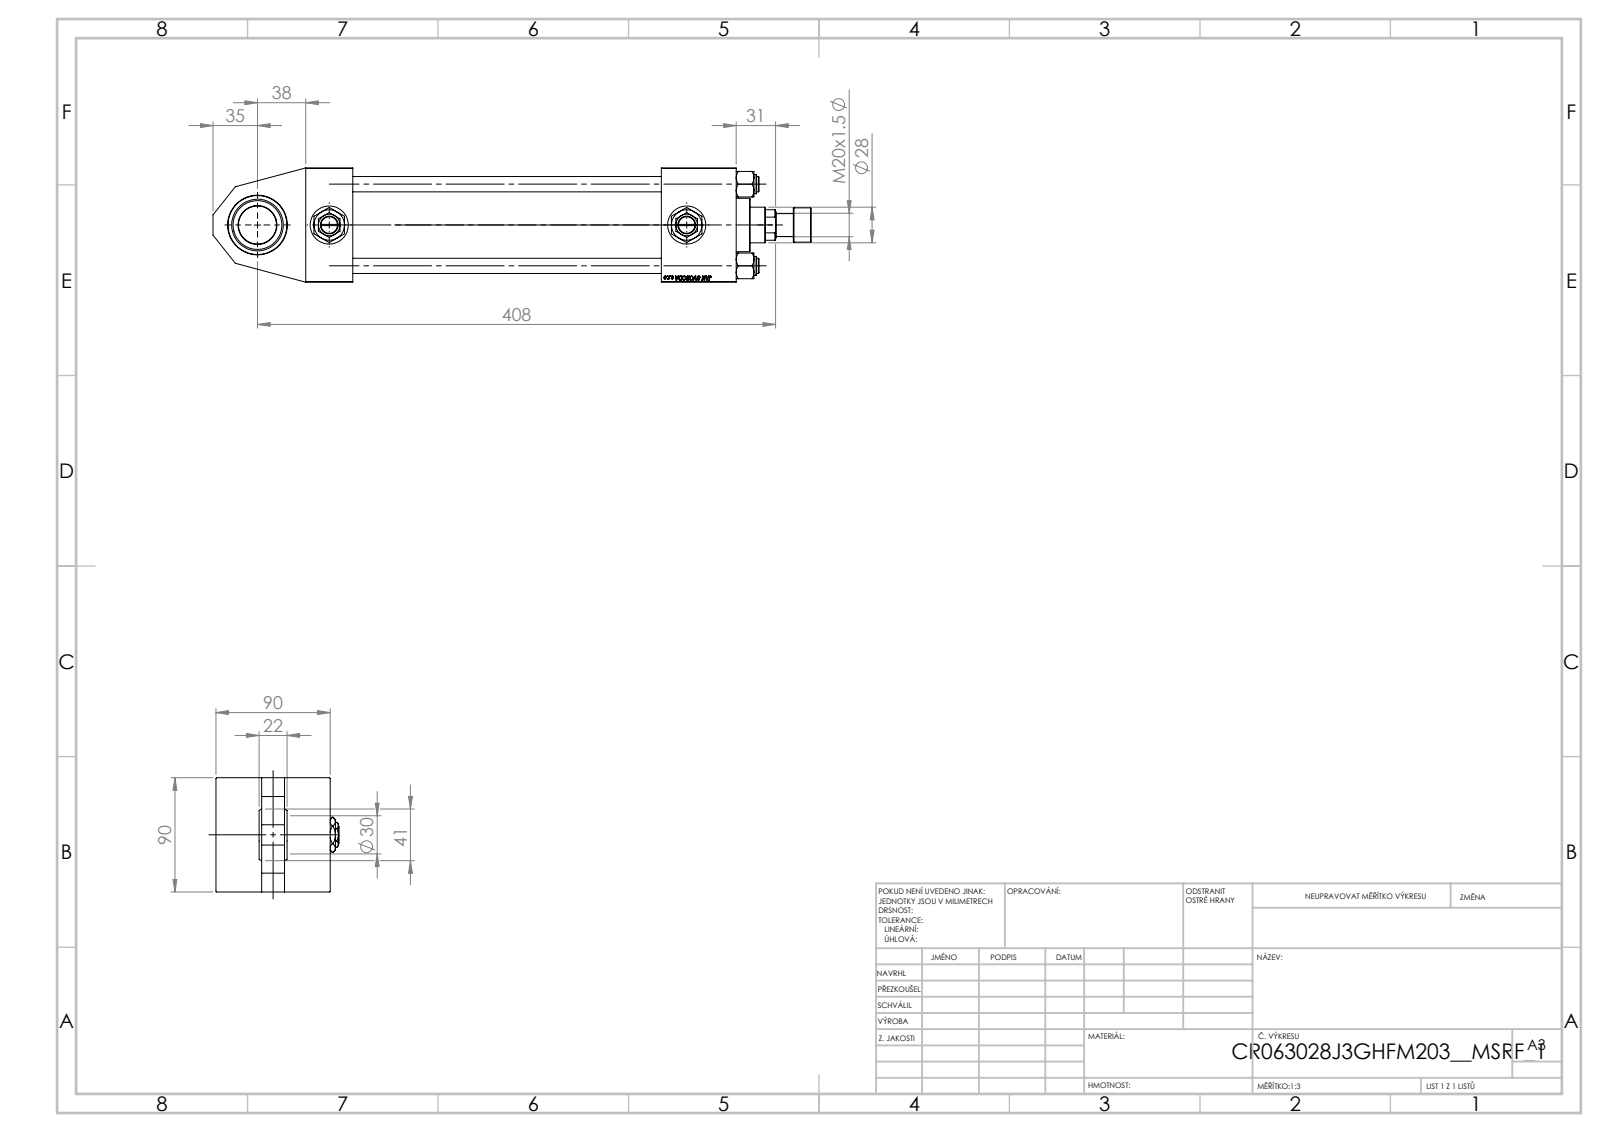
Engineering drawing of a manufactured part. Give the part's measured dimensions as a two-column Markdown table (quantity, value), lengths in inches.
| quantity | value |
| --- | --- |
| part name | V215CR_ROD_END_F; NUT_M5_J; V215CR_J_Body; V215CR_J_VNITRNI_KROUZEK (+4 more) |
| STEP written by | SolidWorks 2019 (CONFIG_CONTROL_DESIGN) |
| units | inches |
| bodies | 15 solids, 1260 faces (568 planar, 104 cylindrical, 588 other) |
| overall size | 18.543 × 3.819 × 3.543 |
| volume | 82.2 in³ |
| surface area | 508.8 in² |
| round holes (diameter × count) | 0.472 × 4, 1.181 × 3, 0.098 × 2, 0.276 × 2, 0.825 × 2, 0.728 × 1, 1.102 × 1, 1.22 × 1, 1.85 × 1, 1.969 × 1, 2.362 × 1, 2.48 × 1 |
| round bosses / shafts (diameter × count) | 0.591 × 4, 2.717 × 1, 1.654 × 1, 1.063 × 1, 0.709 × 1 |
| main face-to-face distances | 3.543, 2.126, 1.417, 11.89, 1.457, 13.346, 2.323, 11.024, 9.567, 0.709 |
| hole center spacings | 1.275, 1.79, 2.531, 2.694, 1.112, 2.224, 3.58, 11.083 |
